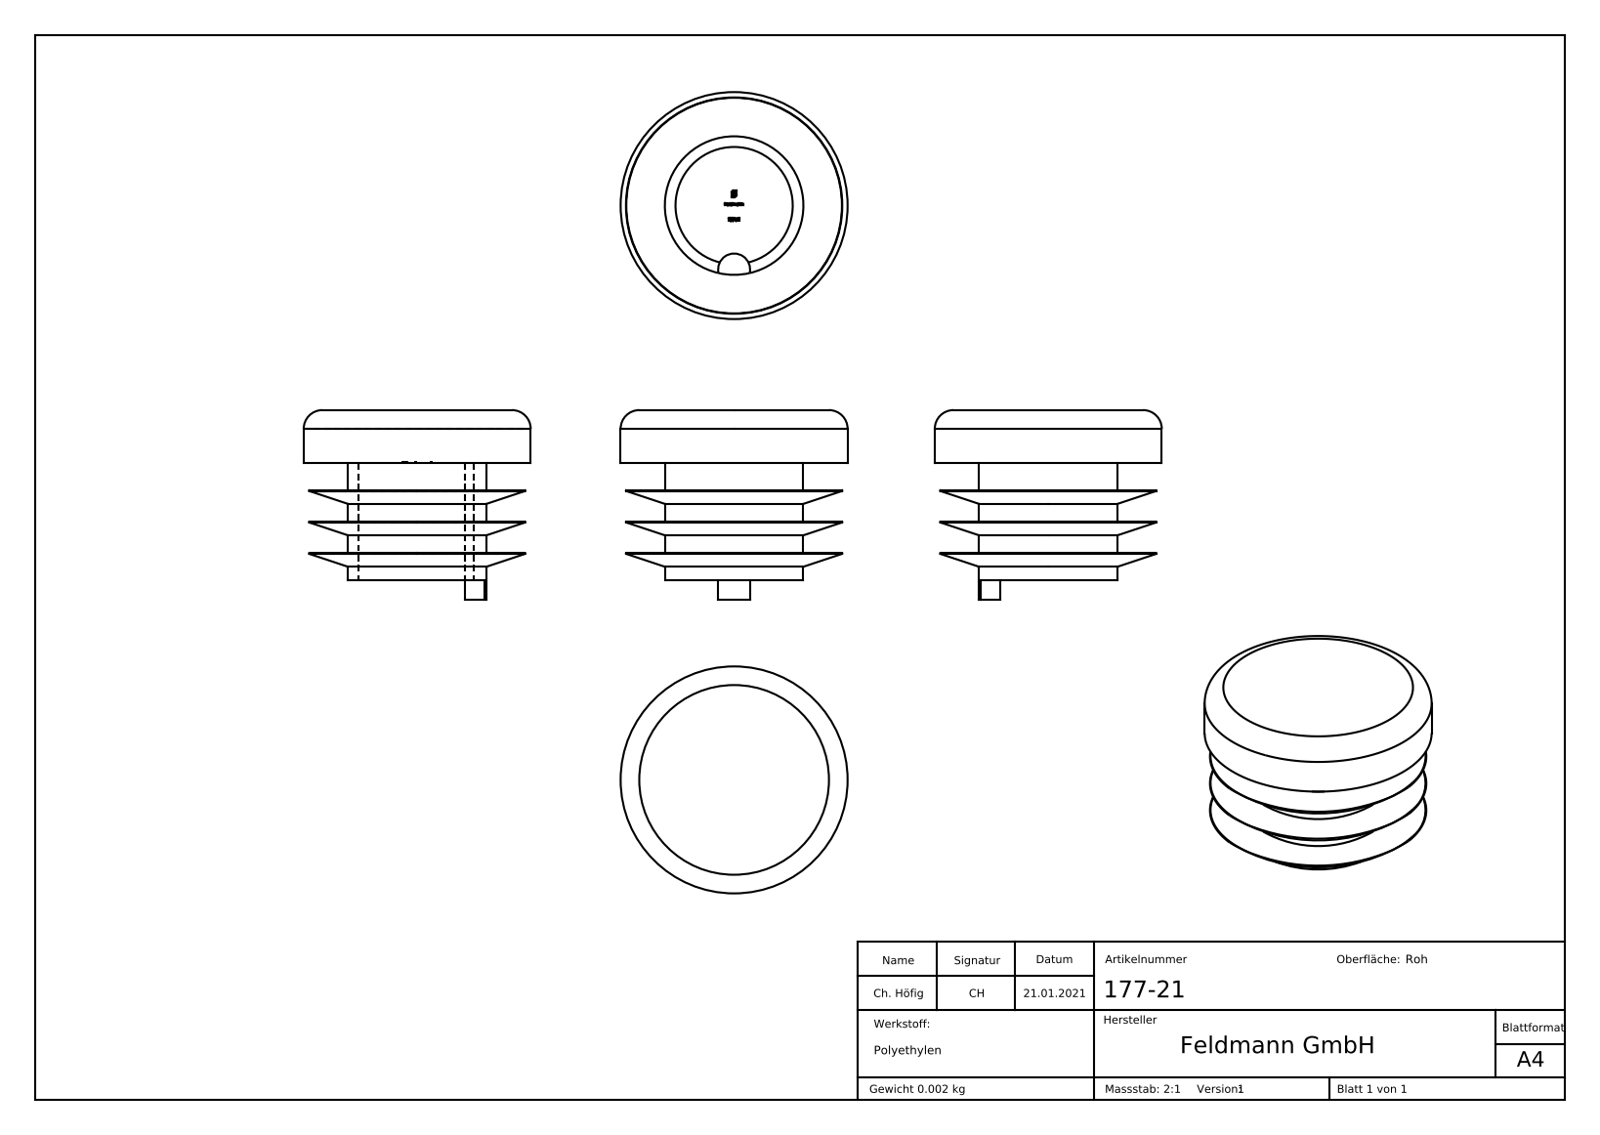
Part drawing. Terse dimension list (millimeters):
name: 177-21
written by: SolidWorks 2018 (CONFIG_CONTROL_DESIGN)
unit: mm
bodies: 1 solid, 222 faces (134 planar, 7 cylindrical, 81 other)
size: 21.3 × 21.3 × 17.8
volume: 2 555 mm³; area: 2 876 mm²
holes: 1× ⌀11
bosses: 1× ⌀21.3, 1× ⌀13
rounds: 1× R1.5
face distances: 2.95, 5, 5.45, 10.45, 5.9, 8.4, 13.4, 2.5, 7.5, 2.6
